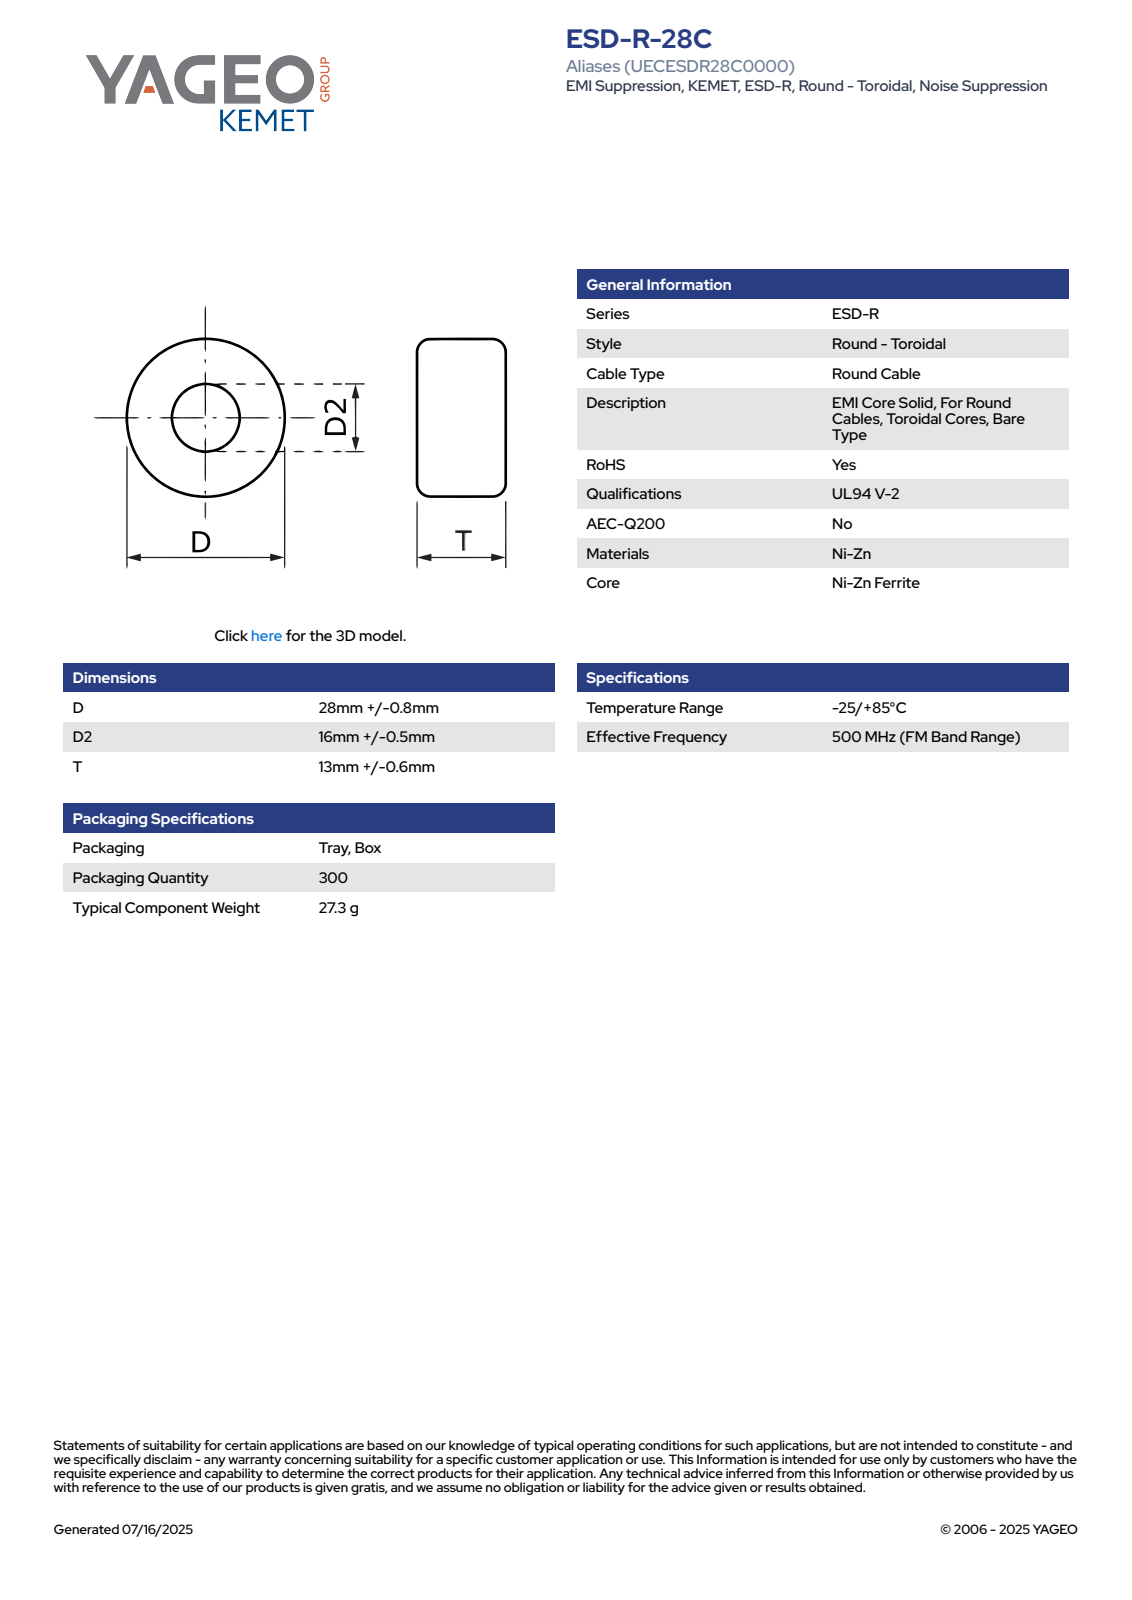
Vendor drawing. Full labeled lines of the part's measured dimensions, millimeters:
Part name (STEP PRODUCT): EC_KBC_D28.8D216T13.6
STEP written by: SolidWorks 2021 (AUTOMOTIVE_DESIGN)
Units: millimetres
Bodies: 1 solid, 66 faces (24 planar, 7 cylindrical, 35 other)
Overall size (bounding box): 28.81 × 28.8 × 13.6
Volume: 6 094 mm³ · Surface area: 2 752 mm²
Round holes (diameter × count): ⌀16 ×1
Round bosses / shafts (diameter × count): ⌀28.8 ×1
Partial cylindrical surfaces — rounded edges, fillets, slot ends (radius × count): R14.41 ×1
Main face-to-face distances: 13.6, 5.95, 7.65, 1.7, 0.32, 6.27, 7.33, 1.38, 1.06, 7.01
